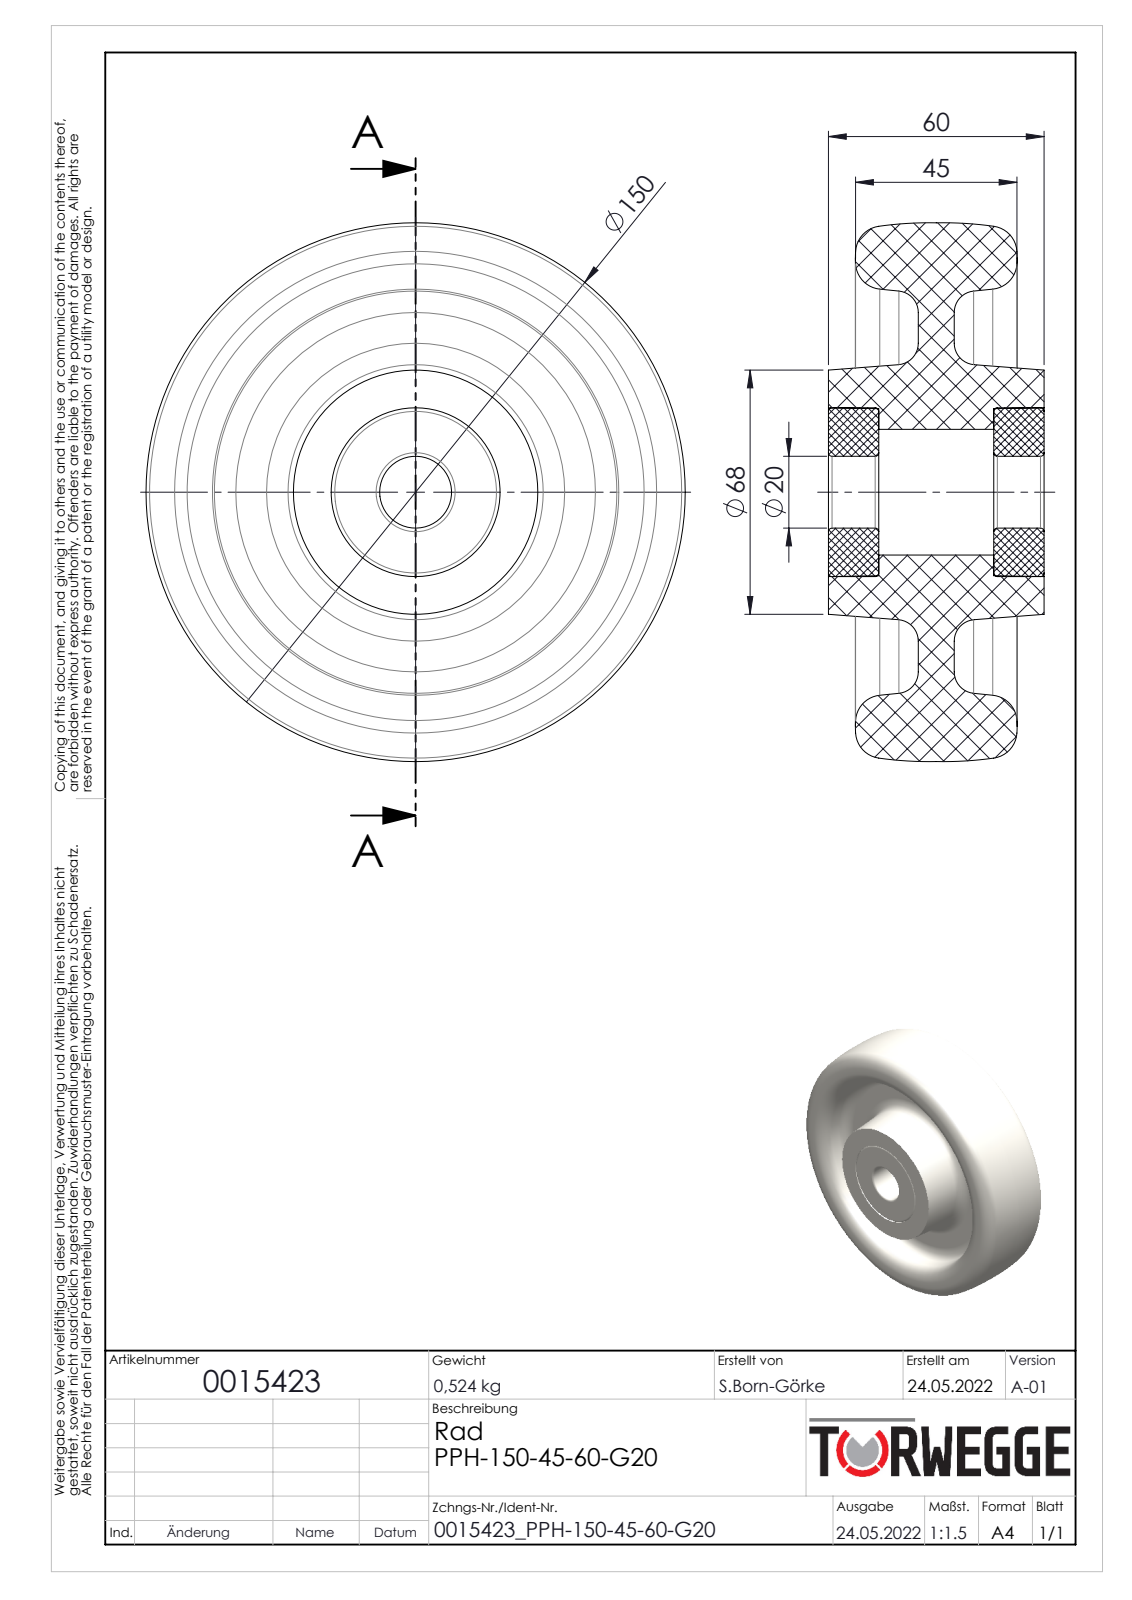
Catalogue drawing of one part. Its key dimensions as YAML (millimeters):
part_name: "0015423"
step_written_by: "SolidWorks 2020 (AUTOMOTIVE_DESIGN)"
units: millimeters
bodies: {solids: 3, faces: 72, planar: 10, cylindrical: 10, other: 52}
overall_size: [150.04, 150.04, 60]
volume: 578322
surface_area: 86582
round_holes:
  - {diameter: 20, count: 1}
  - {diameter: 35, count: 1}
round_bosses_or_shafts:
  - {diameter: 47, count: 1}
face_to_face_distances: [25, 35, 14, 46, 11, 21, 60, 10, 32]
